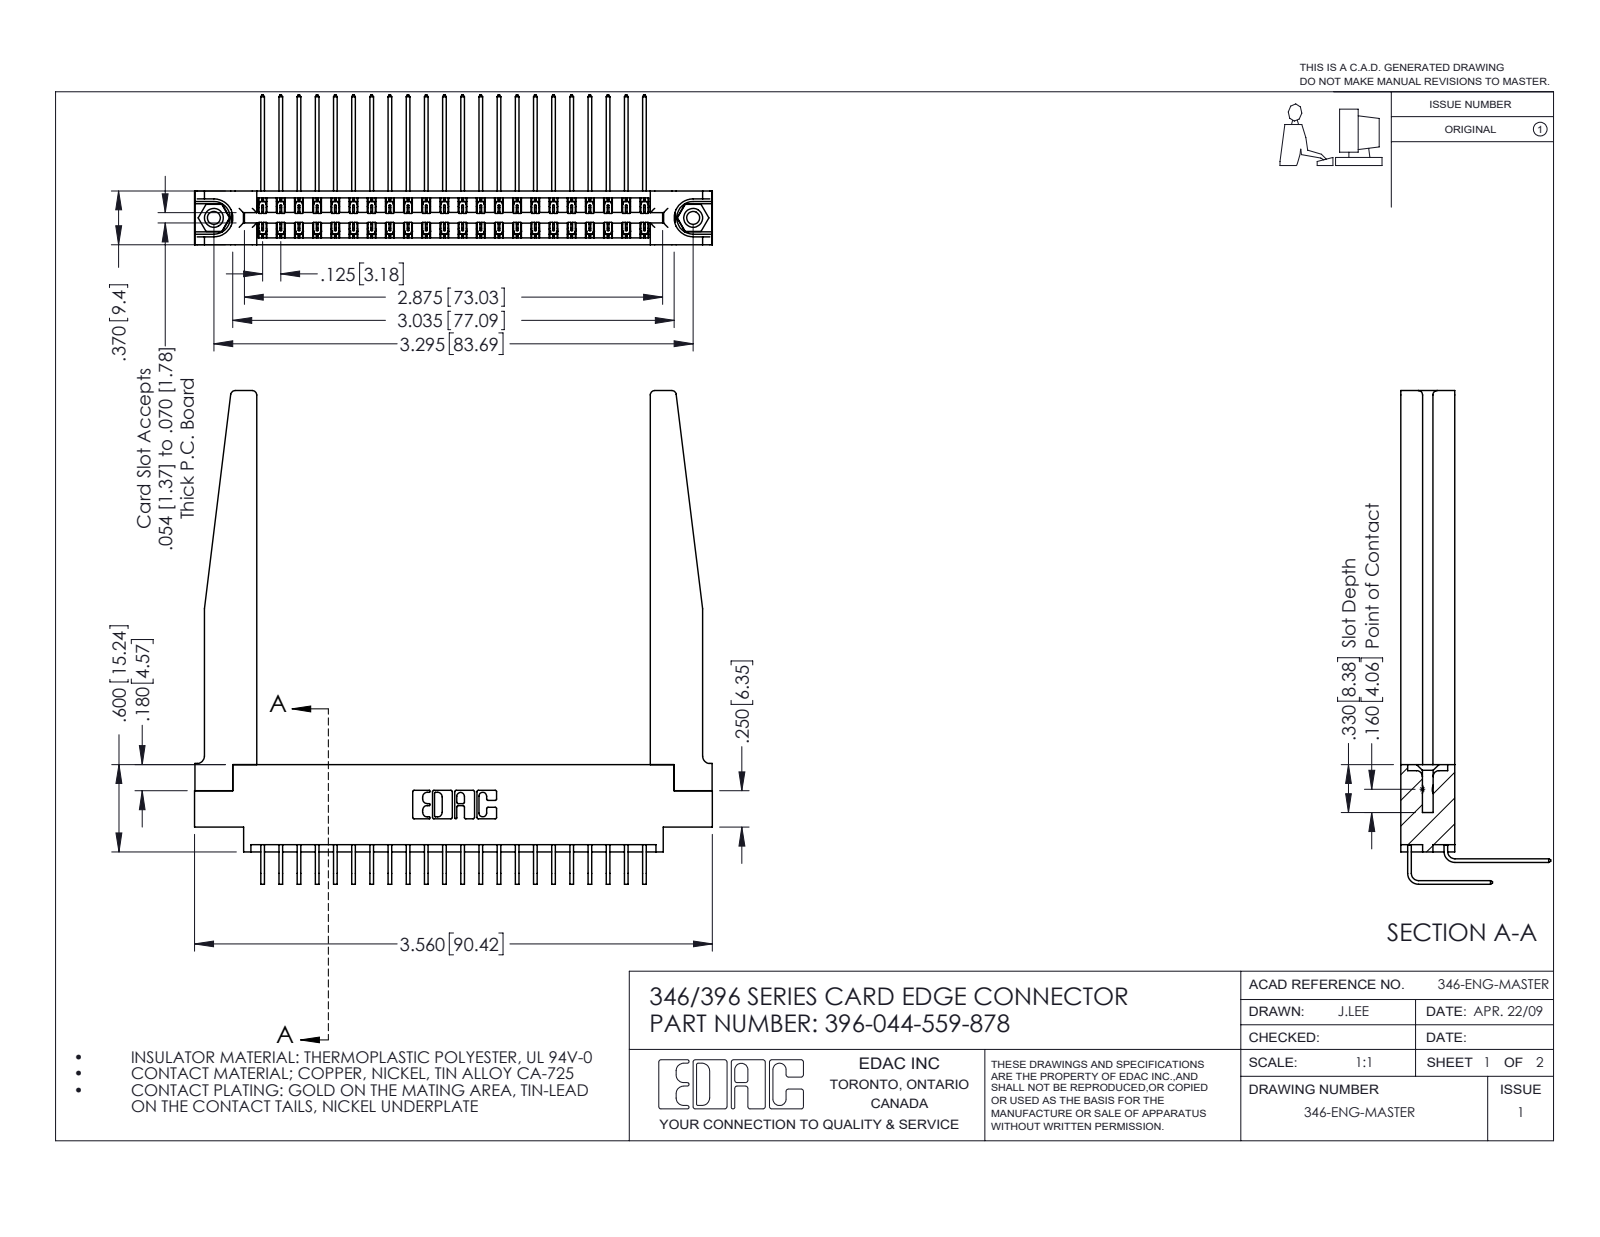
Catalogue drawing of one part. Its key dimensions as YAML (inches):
part_name: "346-220-078_345-220-078; 345-292-001_558 559 Tail - 1; 345-292-001_559 Tail - 2; 345-250-001_345-250-001-102 (+2 more)"
step_written_by: "SolidWorks 2016 (CONFIG_CONTROL_DESIGN)"
units: inches
bodies: {solids: 49, faces: 2736, planar: 1850, cylindrical: 834, other: 52}
overall_size: [3.56, 3.393, 1.03]
volume: 0.956
surface_area: 30.48
round_holes:
  - {diameter: 0.089, count: 2}
  - {diameter: 0.125, count: 2}
  - {diameter: 0.156, count: 2}
  - {diameter: 0.064, count: 1}
round_bosses_or_shafts:
  - {diameter: 0.155, count: 2}
partial_cylinders:
  - {radius: 0.006, count: 66}
  - {radius: 0.01, count: 22}
  - {radius: 0.03, count: 8}
  - {radius: 0.007, count: 6}
  - {radius: 0.031, count: 6}
  - {radius: 0.05, count: 4}
  - {radius: 0.026, count: 3}
  - {radius: 0.014, count: 2}
face_to_face_distances: [0.37, 0.048, 0.072, 0.322, 0.148, 0.15, 0.025, 0.25, 0.298, 0.275]
hole_center_spacings: [0.246, 3.087, 3.295]
